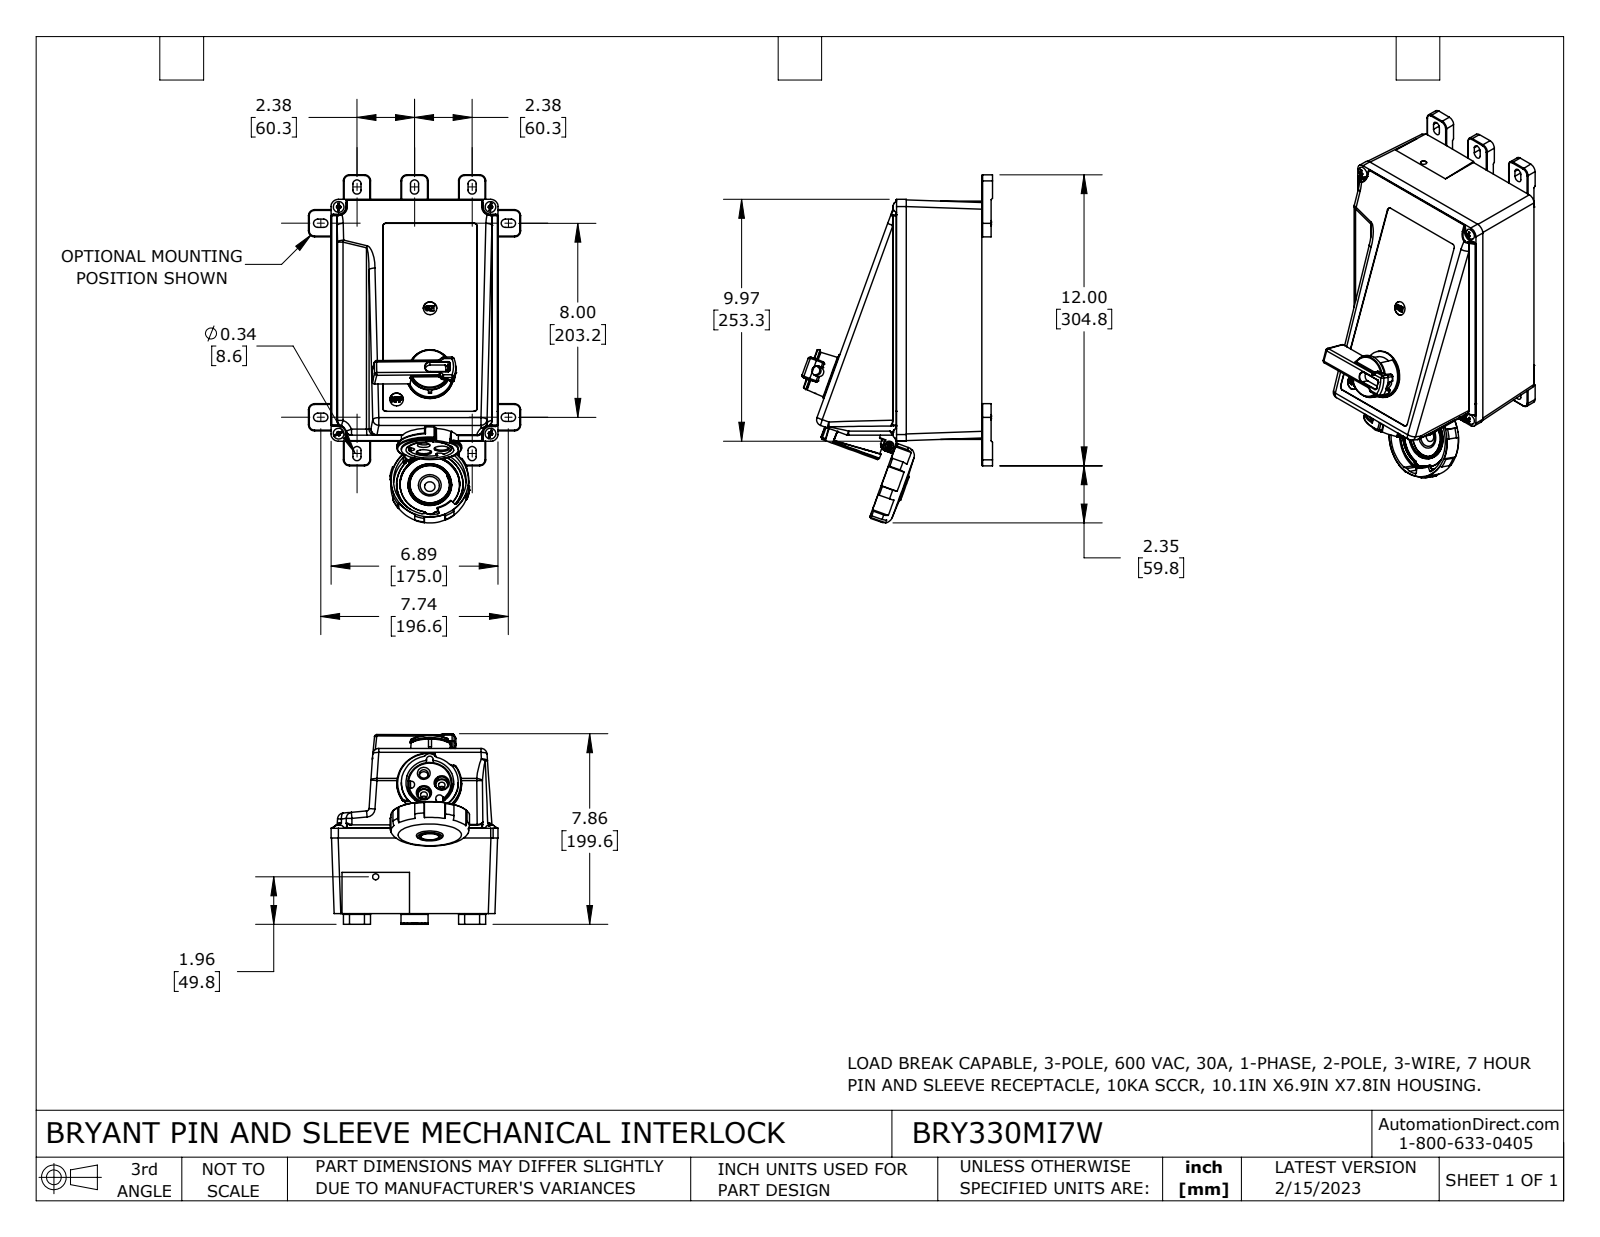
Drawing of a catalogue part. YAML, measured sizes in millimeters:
part_name: "BRY330MI7W"
step_written_by: "SolidWorks 2021 (CONFIG_CONTROL_DESIGN)"
units: millimeters
bodies: {solids: 10, faces: 2055, planar: 731, cylindrical: 673, other: 651}
overall_size: [364.6, 199.6, 175]
volume: 5522000
surface_area: 303400
round_holes:
  - {diameter: 7.1, count: 5}
  - {diameter: 2, count: 4}
  - {diameter: 4, count: 2}
  - {diameter: 14.2, count: 2}
  - {diameter: 2.6, count: 1}
  - {diameter: 3.5, count: 1}
  - {diameter: 4, count: 1}
  - {diameter: 6.4, count: 1}
  - {diameter: 6.9, count: 1}
  - {diameter: 16.8, count: 1}
  - {diameter: 19.6, count: 1}
  - {diameter: 21.8, count: 1}
round_bosses_or_shafts:
  - {diameter: 6.7, count: 2}
  - {diameter: 3.1, count: 2}
  - {diameter: 69.6, count: 1}
  - {diameter: 59.7, count: 1}
  - {diameter: 48.8, count: 1}
  - {diameter: 47, count: 1}
  - {diameter: 46.5, count: 1}
  - {diameter: 45.6, count: 1}
partial_cylinders:
  - {radius: 0.4, count: 124}
  - {radius: 0.8, count: 54}
  - {radius: 2, count: 30}
  - {radius: 6.4, count: 24}
  - {radius: 2.3, count: 17}
  - {radius: 0.3, count: 16}
  - {radius: 0.5, count: 13}
  - {radius: 1.9, count: 12}
face_to_face_distances: [3, 4.4, 245.2, 120.7, 249.7, 105.9, 105.6, 3.8, 9.7, 0.9]
hole_center_spacings: [17.8, 17.8, 20, 21.6, 68.2, 84, 120.7, 203.2]
